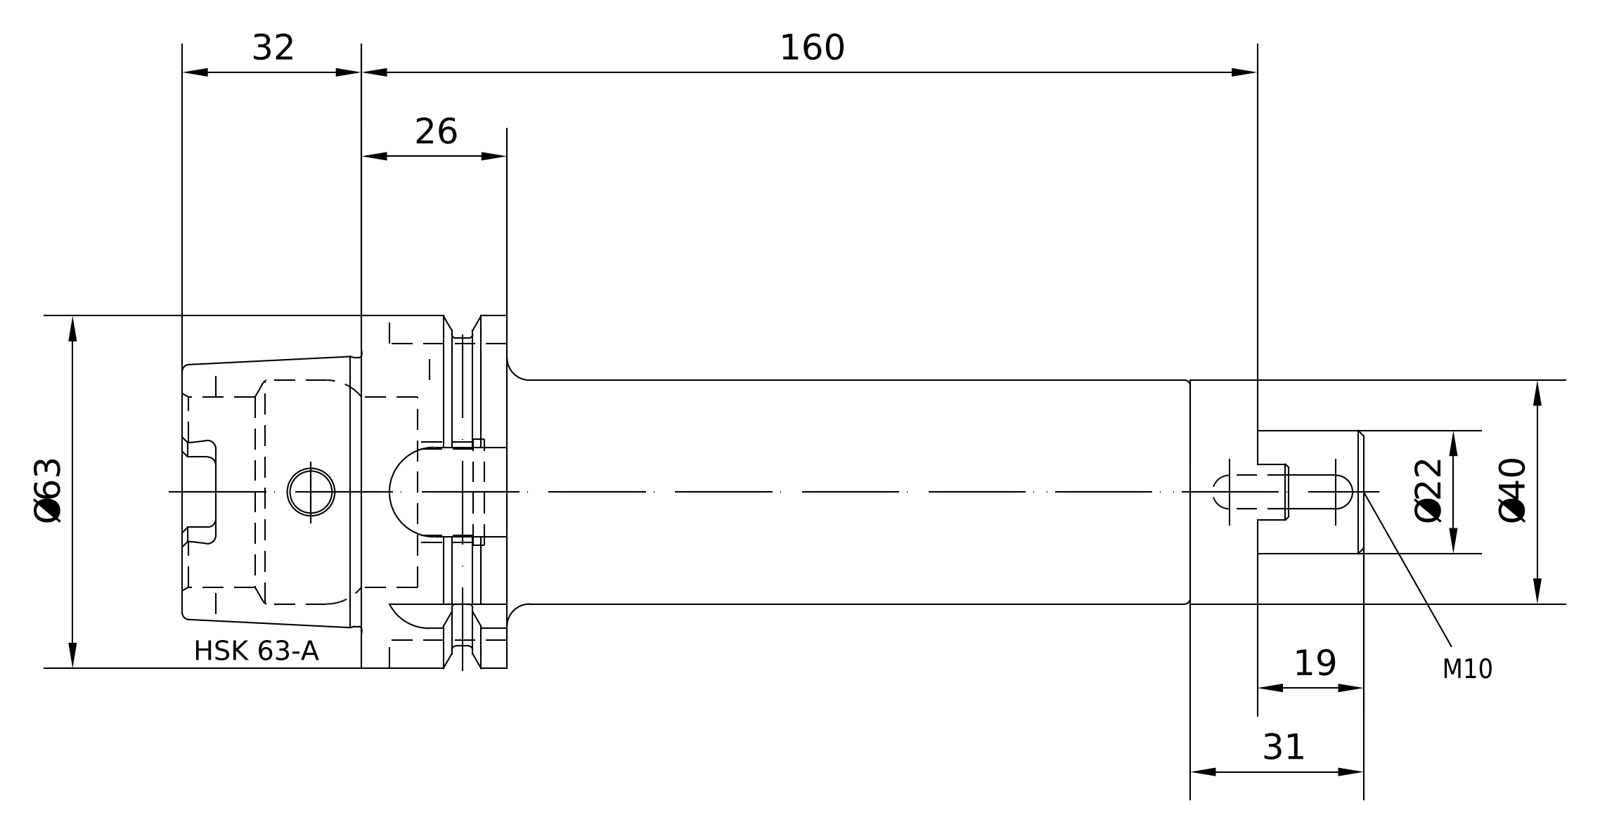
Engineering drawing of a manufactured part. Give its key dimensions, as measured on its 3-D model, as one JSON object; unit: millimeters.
{"part_name": "A63-042-22; 85-200-22; A63-042-22_ASM", "step_written_by": "PRO/ENGINEER BY PARAMETRIC TECHNOLOGY CORPORATION, 2010430 (CONFIG_CONTROL_DESIGN)", "units": "millimeters", "bodies": {"solids": 2, "faces": 265, "planar": 123, "cylindrical": 64, "other": 78}, "overall_size": [211, 63, 63], "volume_mm3": 253555, "surface_area_mm2": 47280, "round_holes": [[10, 2], [7.5, 1], [8.5, 1], [16.92, 1], [18.32, 1], [18.66, 1], [22.36, 1], [26, 1], [34, 1]], "round_bosses_or_shafts": [[63, 1], [55, 1], [48.04, 1], [40, 1], [22, 1], [18, 1]], "partial_cylinders_radius": [[1.5, 6], [3, 6], [5.05, 1], [8, 1], [8.02, 1], [9.02, 1]], "face_to_face_distances": [148, 26, 122, 10, 160, 134, 12, 16, 138, 150]}
